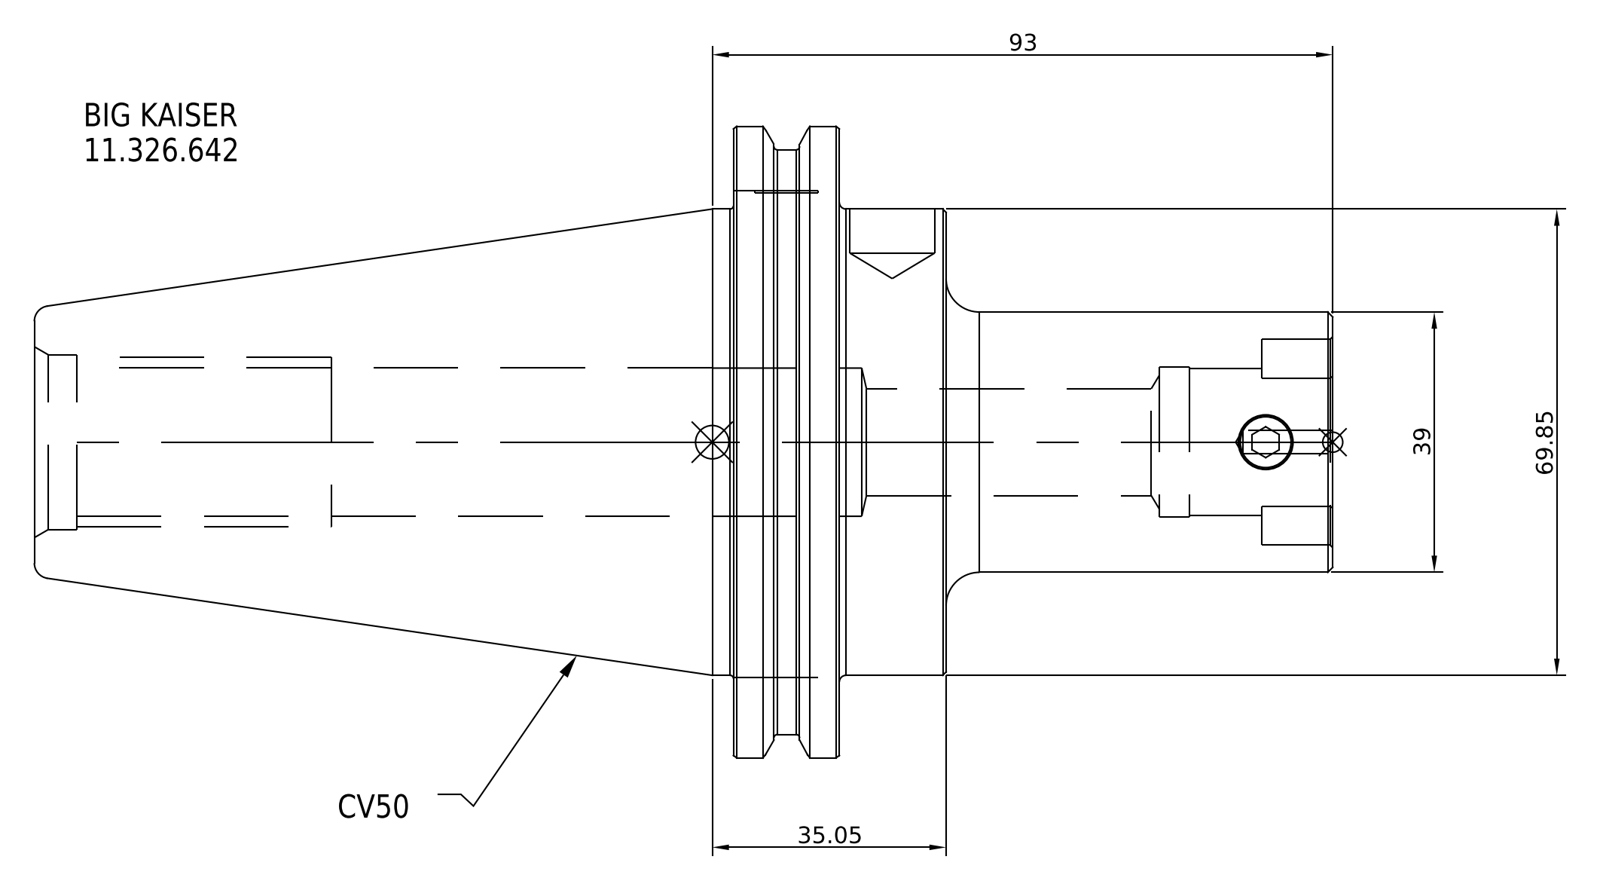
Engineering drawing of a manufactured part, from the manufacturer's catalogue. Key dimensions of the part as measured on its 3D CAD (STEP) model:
Part name (STEP PRODUCT): 11.326.642
STEP written by: SolidWorks 2021 (CONFIG_CONTROL_DESIGN)
Units: millimetres
Bodies: 1 solid, 16 faces (7 planar, 6 cylindrical, 3 other)
Overall size (bounding box): 194.6 × 98.43 × 98.43
Volume: 511 767 mm³ · Surface area: 48 079 mm²
Round bosses / shafts (diameter × count): ⌀98.43 ×1, ⌀91.29 ×1, ⌀69.85 ×1, ⌀39 ×1
Main face-to-face distances: 17.55, 15.95, 33.5, 136.6, 120.65, 103.1, 58, 73.95, 91.5, 194.6
